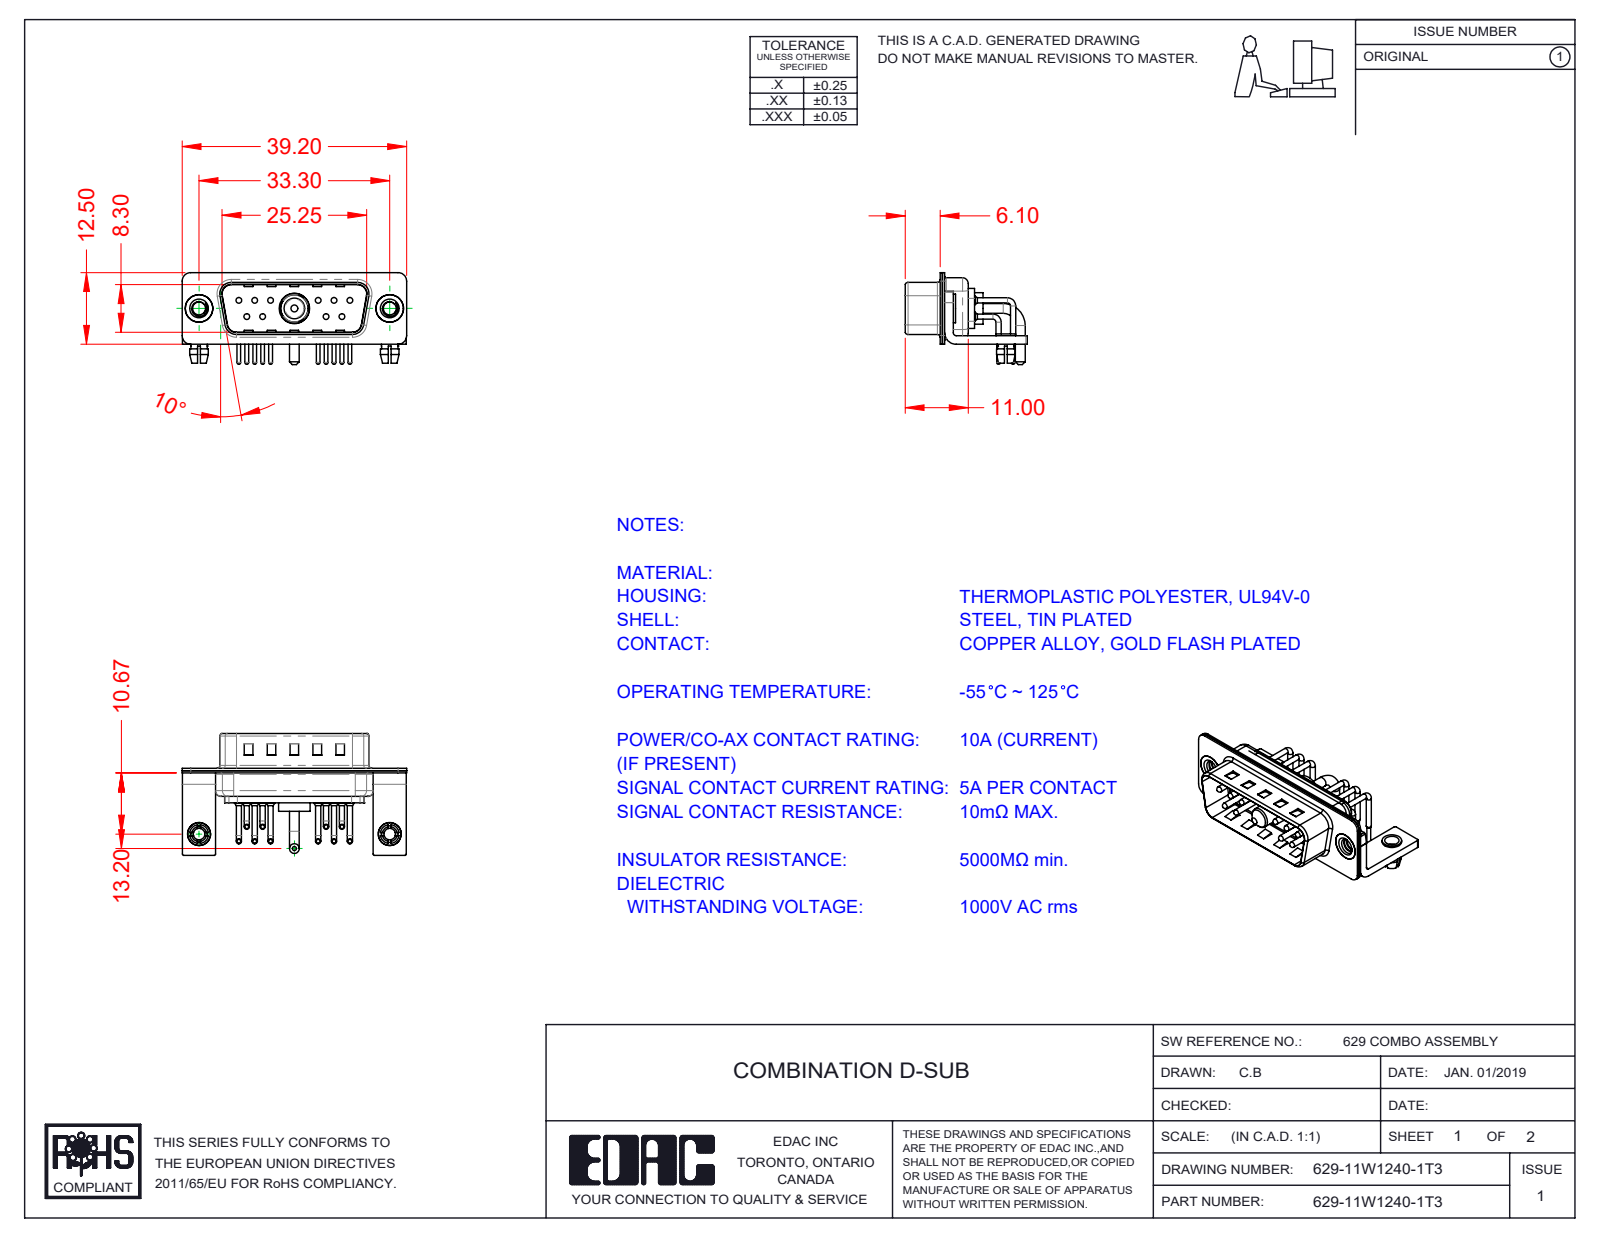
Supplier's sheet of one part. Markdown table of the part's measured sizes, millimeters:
| quantity | value |
| --- | --- |
| part name | 629Combo Board Lock; 629Combo Contact Row 1; Power Pin_10A RA; 629-11W1240-1T3 (+6 more) |
| STEP written by | SolidWorks 2020 (CONFIG_CONTROL_DESIGN) |
| units | millimeters |
| bodies | 21 solids, 1628 faces (866 planar, 568 cylindrical, 194 other) |
| overall size | 39.2 × 21.3 × 16.05 |
| volume | 2 309 mm³ |
| surface area | 5 980 mm² |
| round holes (diameter × count) | 2 × 12, 0.75 × 10, 1.6 × 10, 2.26 × 2, 2.5 × 2, 3.2 × 2, 4 × 2, 4.8 × 2, 4.85 × 1, 5.3 × 1 |
| round bosses / shafts (diameter × count) | 0.9 × 20, 1.5 × 10, 1 × 10, 0.65 × 10, 5 × 2, 4.9 × 2, 4 × 2, 3.4 × 2 |
| partial cylindrical surfaces (radius × count) | 0.25 × 16, 1.5 × 16, 2 × 13, 1.01 × 10, 0.5 × 9, 1.6 × 8, 1 × 7, 0.6 × 4 |
| main face-to-face distances | 0.4, 0.8, 1.5, 9.5, 9.1, 8.7, 9.9, 0.6, 1.9, 5.2 |
| hole center spacings | 3.16, 2.77, 13.85, 11.08, 16.62, 5.03, 5.04, 5.54 |
